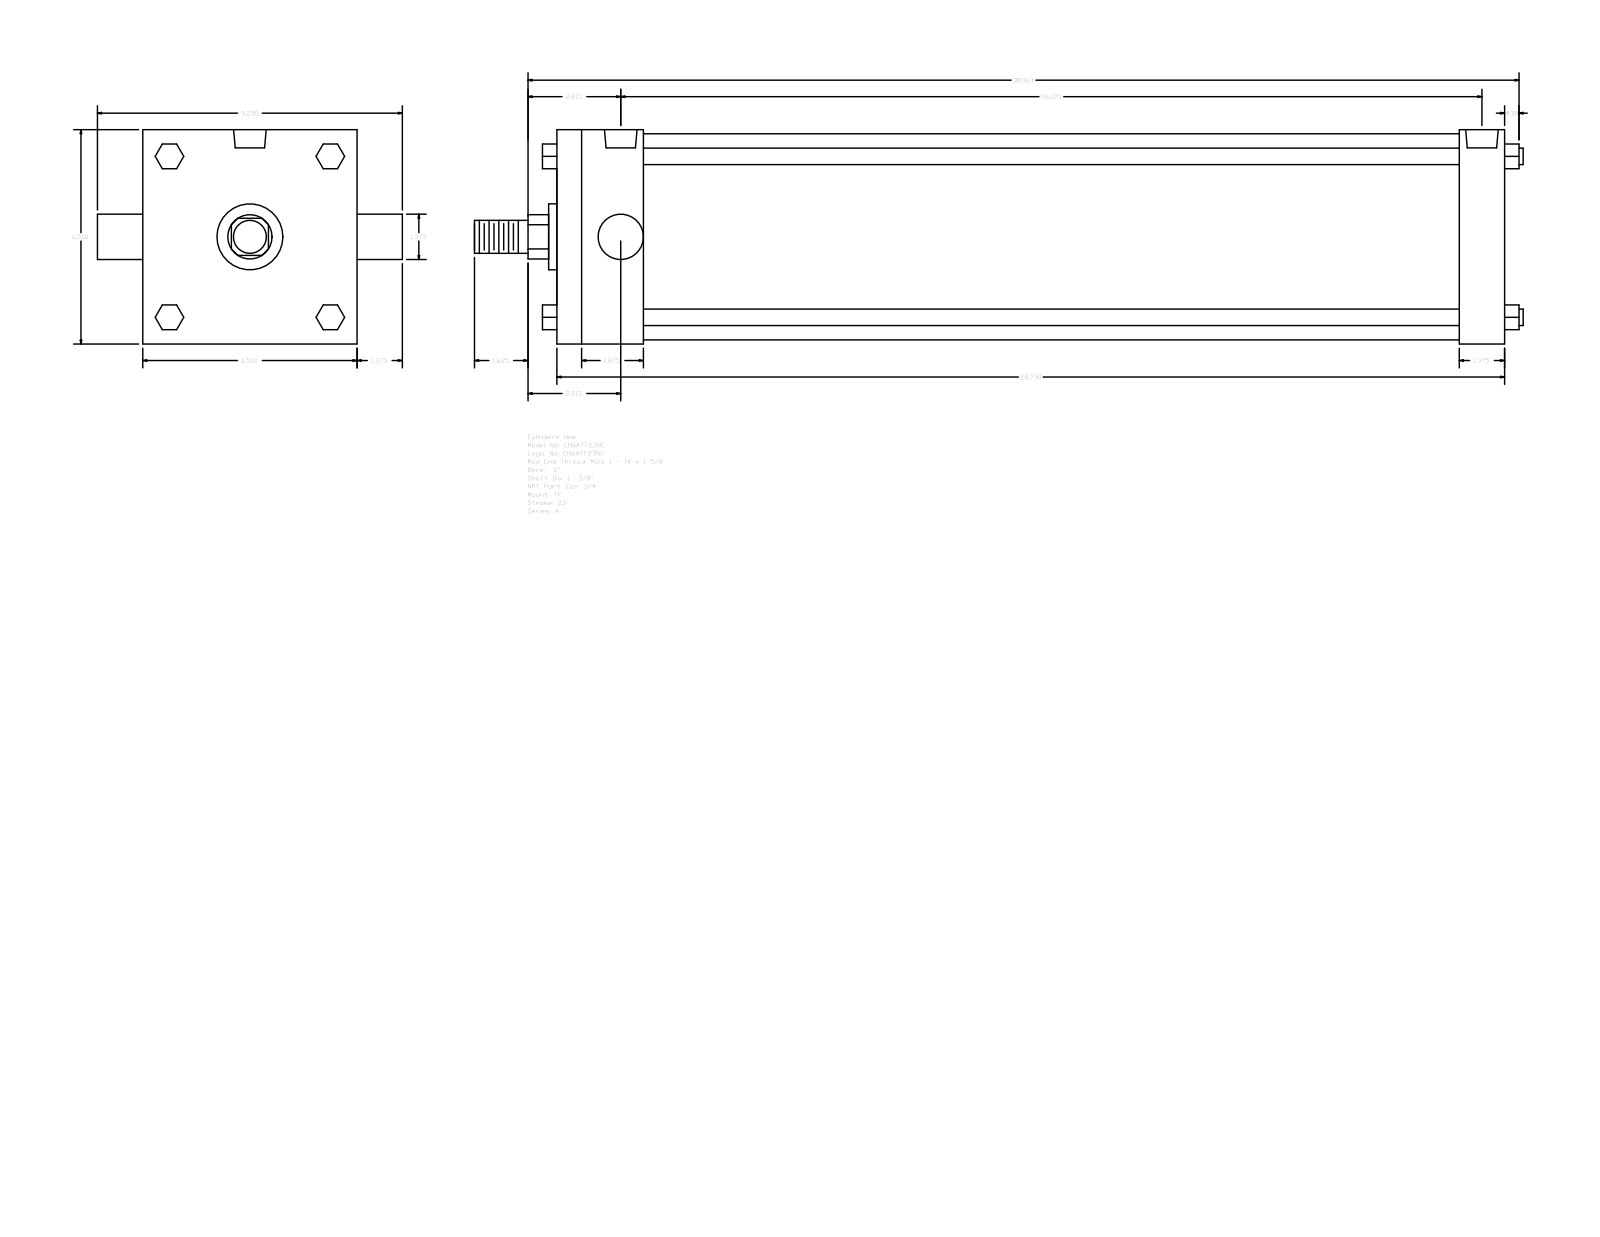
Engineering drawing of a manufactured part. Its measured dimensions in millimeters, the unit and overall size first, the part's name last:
Units: millimetres
Overall size (bounding box): 808.04 × 234.95 × 165.1
Round holes (diameter × count): ⌀15.08 ×3, ⌀25.12 ×2
Round bosses / shafts (diameter × count): ⌀12.7 ×4, ⌀34.92 ×2, ⌀158.75 ×1, ⌀50.8 ×1, ⌀25.4 ×1
Partial cylindrical surfaces — rounded edges, fillets, slot ends (radius × count): R17.06 ×1
Main face-to-face distances: 165.1, 730.25, 66.67, 663.58, 695.32, 628.65, 34.93, 19.05, 61.97, 107.34
Hole centre spacings: 5.56, 658.01, 652.45, 663.57
Bodies: 0 solids, 120 faces (92 planar, 28 cylindrical, 0 other)
Part name (STEP PRODUCT): A_TF__0600_1.375
STEP written by: GSSL Pune (CONFIG_CONTROL_DESIGN)
